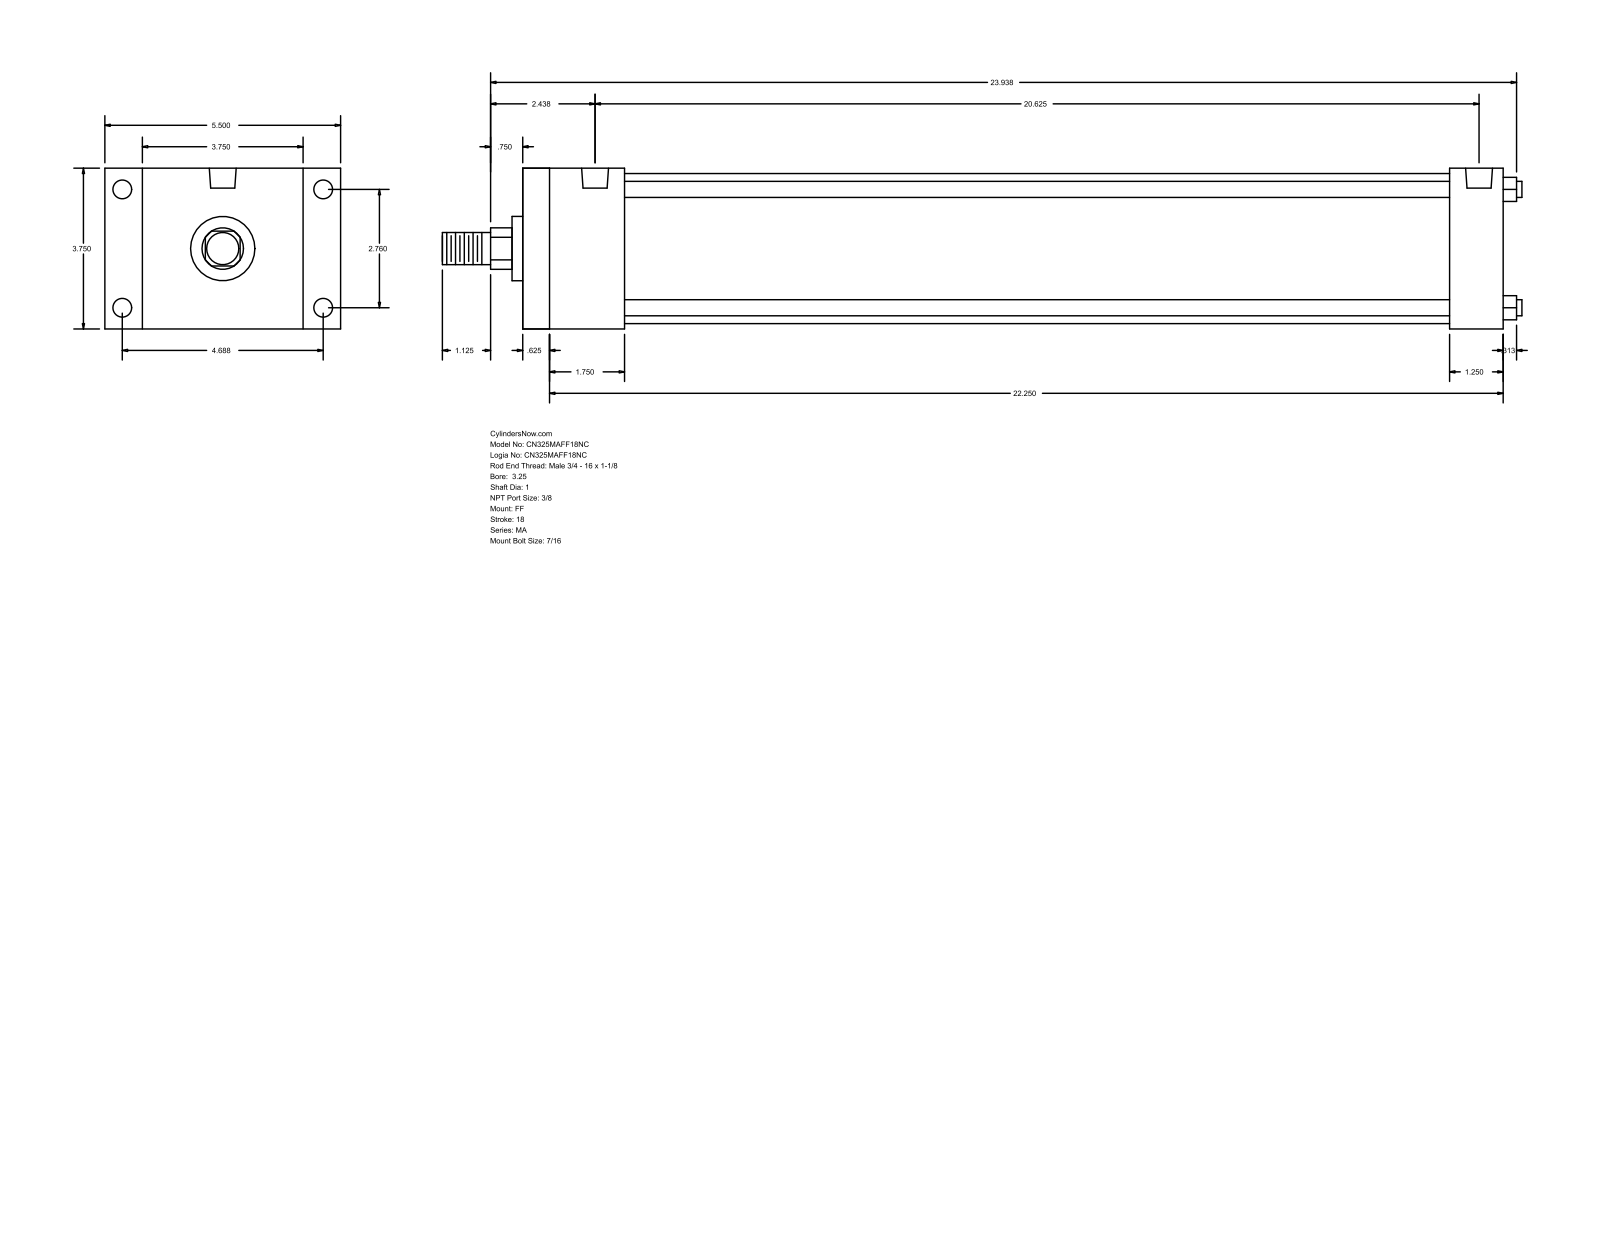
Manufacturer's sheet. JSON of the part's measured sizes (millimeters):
{"part_name": "MA_FF__0325_1", "step_written_by": "GSSL Pune (CONFIG_CONTROL_DESIGN)", "units": "millimeters", "bodies": {"solids": 0, "faces": 92, "planar": 64, "cylindrical": 28, "other": 0}, "overall_size": [639.76, 139.7, 95.25], "round_holes": [[11.11, 8], [15.93, 2]], "round_bosses_or_shafts": [[9.53, 4], [88.9, 1], [38.1, 1], [25.4, 1], [19.05, 1]], "partial_cylinders_radius": [[12.29, 1]], "face_to_face_distances": [95.24, 581.03, 15.87, 565.16, 22.23, 117.47, 60.33, 549.28, 44.46, 533.41], "hole_center_spacings": [70.1, 119.06, 138.16, 514.35, 4.76, 4.77, 519.11, 519.12]}
